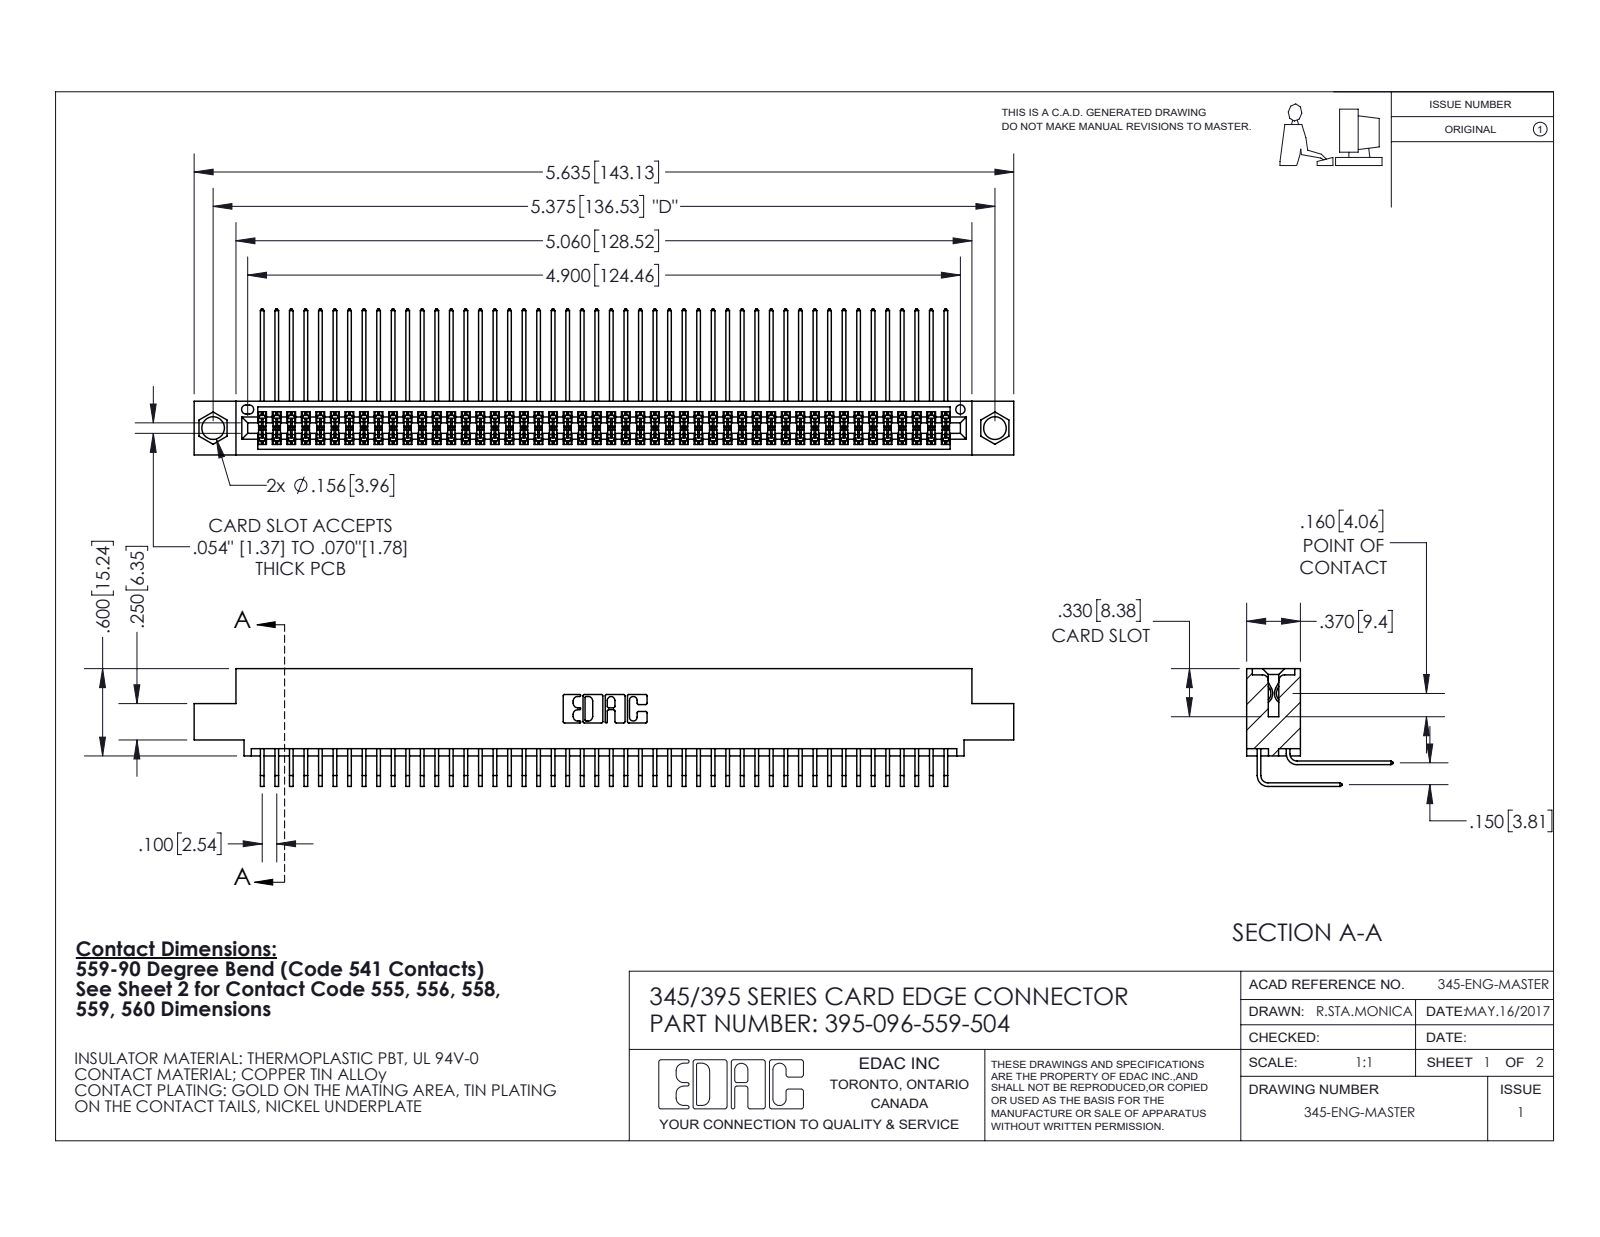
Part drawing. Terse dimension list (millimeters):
name: 345-292-001_559 Tail - 2; 395-096-559-504; 345 Part_0.110 Offset - 0.156 Dia-TI; 345-292-001_558 559 Tail - 1
written by: SolidWorks 2020 (CONFIG_CONTROL_DESIGN)
unit: mm
bodies: 97 solids, 5136 faces (3458 planar, 1678 cylindrical, 0 other)
size: 143.1 × 25.5 × 20.5
volume: 14 300 mm³; area: 23 850 mm²
holes: 2× ⌀4, 1× ⌀1.6
rounds: 192× R0.2, 22× R0.3, 6× R0.2, 6× R0.8, 3× R0.7, 2× R0.4, 2× R0.5, 2× R0.6
face distances: 1.8, 7.6, 5.1, 9.4, 2.5, 6.9, 0.6, 5.7, 4.4, 3.8
hole spacings: 6.9, 130.5, 136.5
